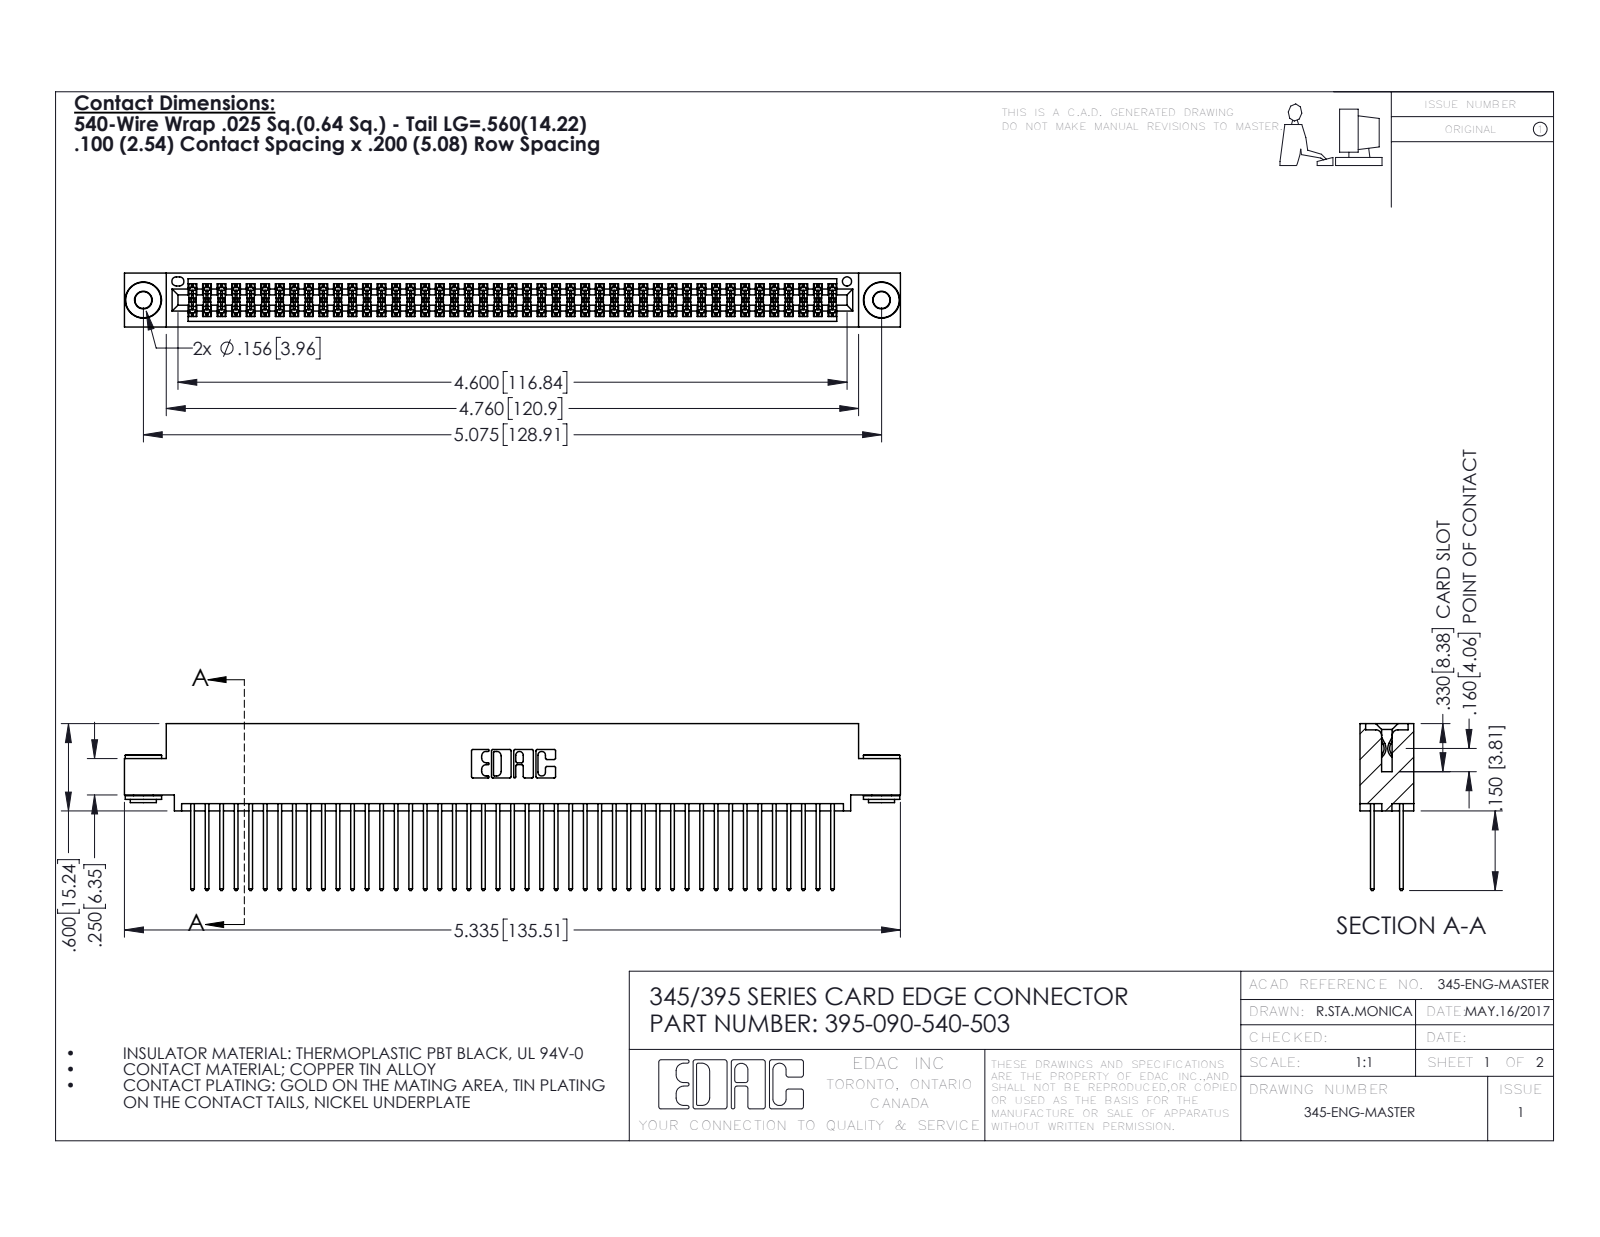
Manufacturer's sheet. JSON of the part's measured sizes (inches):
{"part_name": "345 Part_0.110 Offset - 0.156 Dia-TH; 345-250-002_345-250-002-102; 345-292-001_345-293-140; 395-090-540-503", "step_written_by": "SolidWorks 2016 (CONFIG_CONTROL_DESIGN)", "units": "inches", "bodies": {"solids": 93, "faces": 4668, "planar": 3064, "cylindrical": 1596, "other": 8}, "overall_size": [5.335, 1.147, 0.37], "volume_in3": 0.823, "surface_area_in2": 33.89, "round_holes": [[0.116, 2], [0.156, 2], [0.064, 1]], "round_bosses_or_shafts": [[0.25, 2], [0.18, 2], [0.136, 2]], "partial_cylinders_radius": [[0.006, 135], [0.01, 90], [0.01, 22], [0.007, 6], [0.031, 6], [0.026, 3], [0.014, 2], [0.019, 2]], "face_to_face_distances": [0.072, 0.298, 0.2, 0.025, 0.098, 0.272, 0.37, 0.225, 0.175, 0.149], "hole_center_spacings": [0.27, 4.839, 5.075]}
